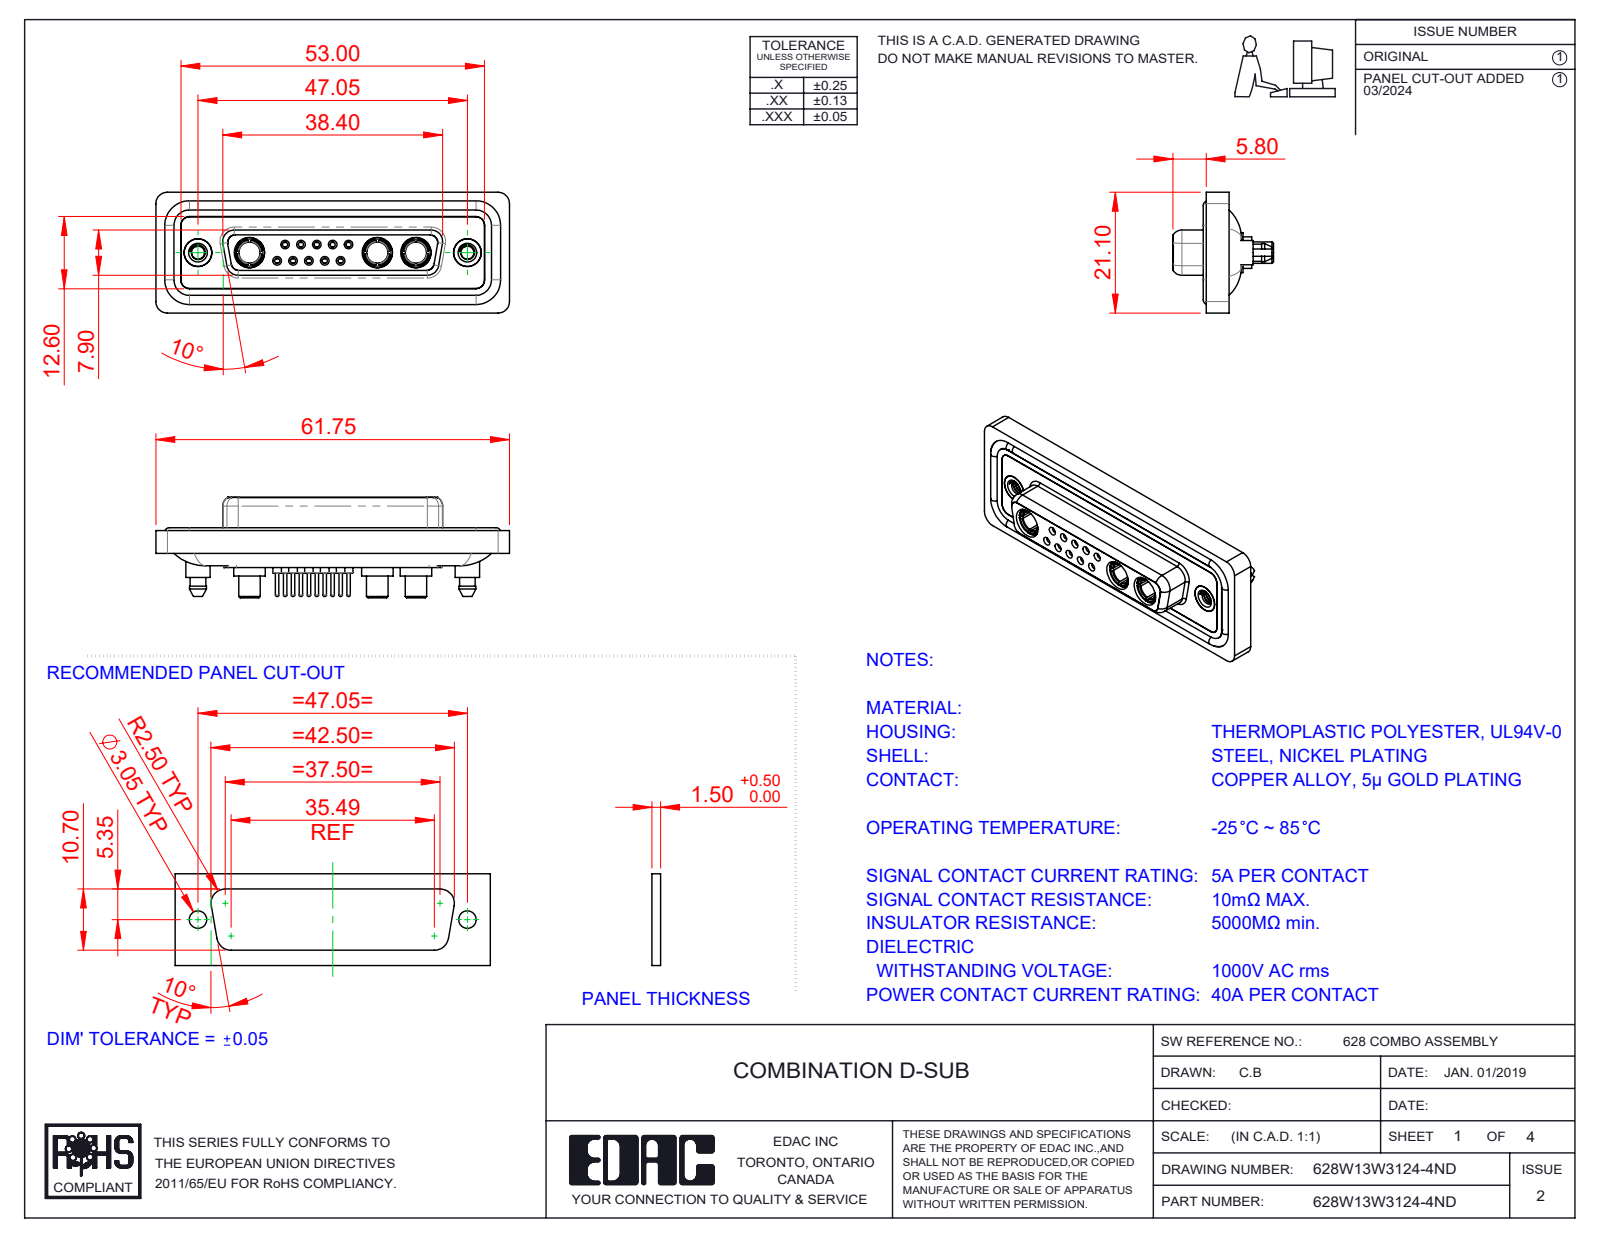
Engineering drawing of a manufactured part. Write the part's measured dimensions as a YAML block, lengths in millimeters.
part_name: "Power Socket_40A S; 628Combo Shell Front_25 Contacts; 628Combo Contact Row 2_24; 628Combo Contact Row 1_24 (+5 more)"
step_written_by: "SolidWorks 2023 (CONFIG_CONTROL_DESIGN)"
units: millimeters
bodies: {solids: 23, faces: 1224, planar: 358, cylindrical: 495, other: 371}
overall_size: [61.75, 21.1, 17.55]
volume: 8464
surface_area: 14081
round_holes:
  - {diameter: 0.9, count: 10}
  - {diameter: 1.1, count: 10}
  - {diameter: 1.5, count: 10}
  - {diameter: 2, count: 10}
  - {diameter: 1.6, count: 5}
  - {diameter: 1.7, count: 5}
  - {diameter: 4.85, count: 5}
  - {diameter: 3.7, count: 3}
  - {diameter: 5.3, count: 3}
  - {diameter: 2.26, count: 2}
  - {diameter: 4, count: 2}
  - {diameter: 4.05, count: 2}
round_bosses_or_shafts:
  - {diameter: 2.2, count: 10}
  - {diameter: 0.6, count: 10}
  - {diameter: 1.6, count: 9}
  - {diameter: 5.5, count: 3}
  - {diameter: 5.2, count: 3}
  - {diameter: 4.96, count: 3}
  - {diameter: 4.75, count: 3}
  - {diameter: 3.75, count: 3}
partial_cylinders:
  - {radius: 1.5, count: 24}
  - {radius: 2, count: 18}
  - {radius: 1.6, count: 10}
  - {radius: 1.35, count: 8}
  - {radius: 0.25, count: 4}
  - {radius: 0.5, count: 4}
  - {radius: 0.6, count: 4}
  - {radius: 0.65, count: 4}
face_to_face_distances: [0.4, 1.8, 7.45, 5.65, 0.5, 6.6, 7.05, 1.6, 2.9, 1.1]
hole_center_spacings: [3.16, 2.77, 5.03, 5.04, 5.54, 8.31, 7.49, 2.76]
